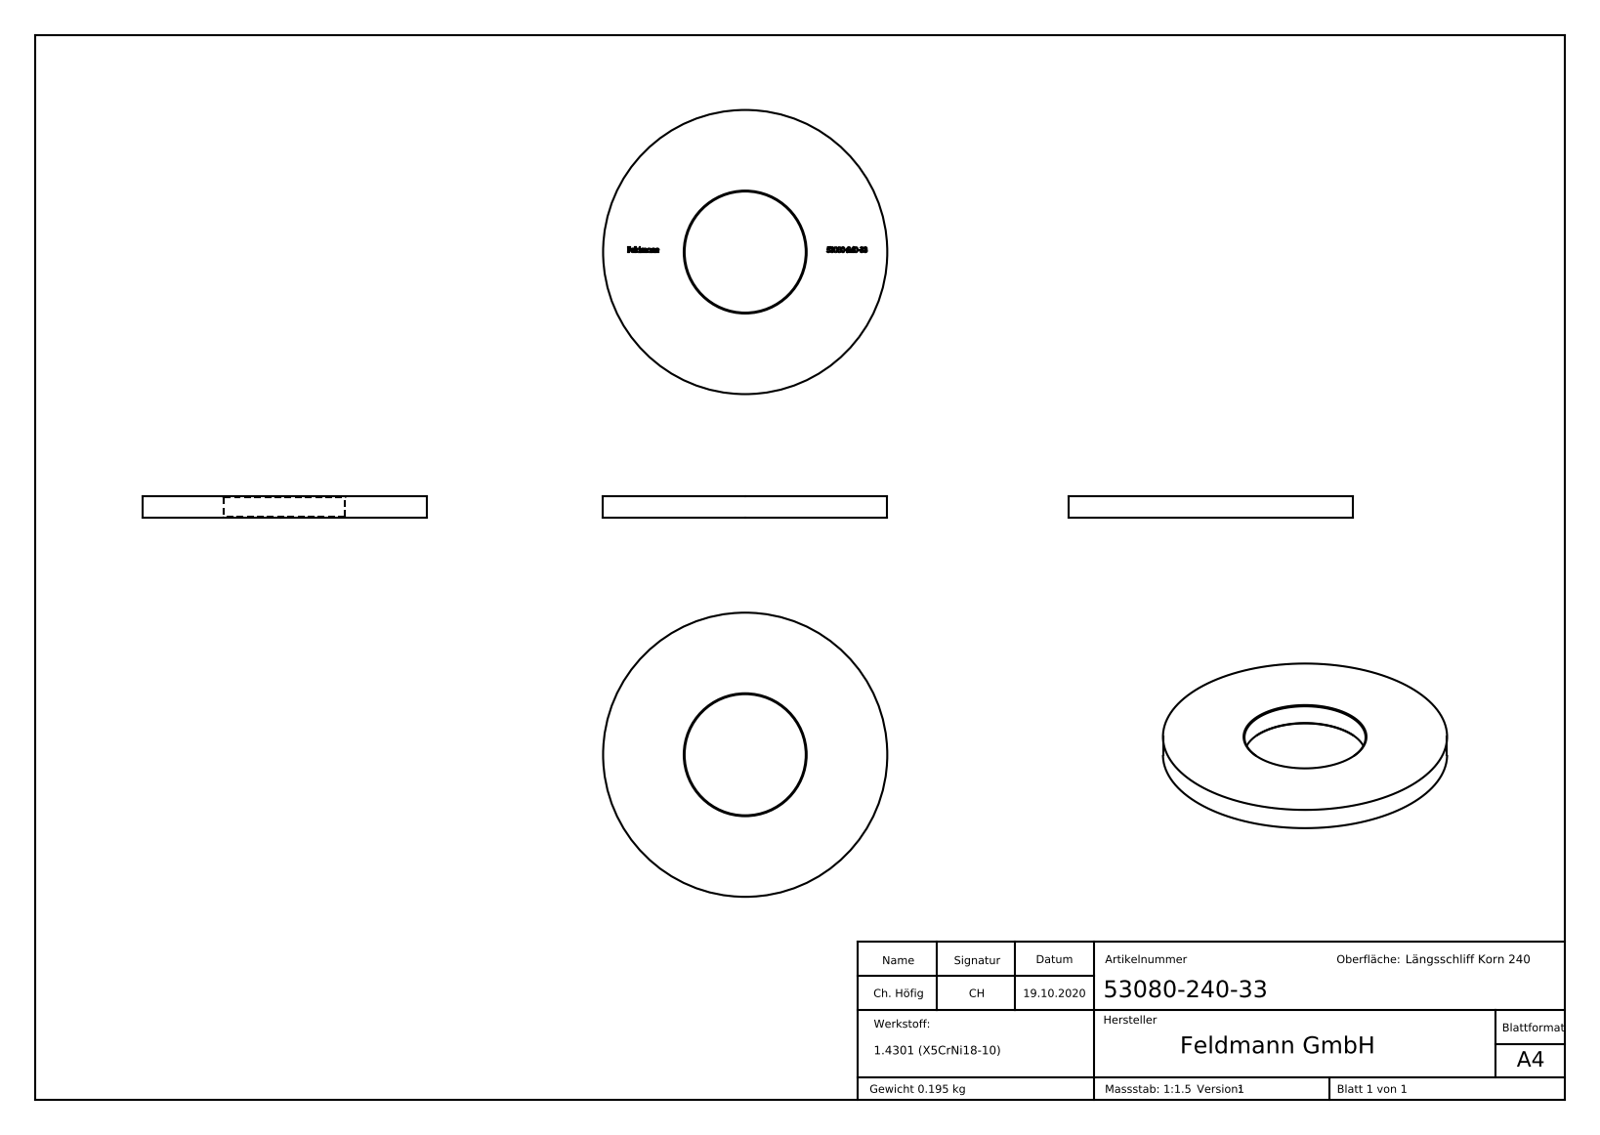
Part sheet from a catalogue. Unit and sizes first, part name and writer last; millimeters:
Units: millimetres
Overall size (bounding box): 80 × 80 × 6
Round holes (diameter × count): ⌀34.1 ×1
Round bosses / shafts (diameter × count): ⌀80 ×1
Main face-to-face distances: 6, 5.9, 0.39, 2.97, 0.44, 0.58, 1.12, 0.88, 1.32, 61.26
Volume: 24 672 mm³ · Surface area: 10 357 mm²
Bodies: 1 solid, 283 faces (127 planar, 4 cylindrical, 152 other)
Part name (STEP PRODUCT): 53080-240-33
STEP written by: SolidWorks 2018 (CONFIG_CONTROL_DESIGN)
